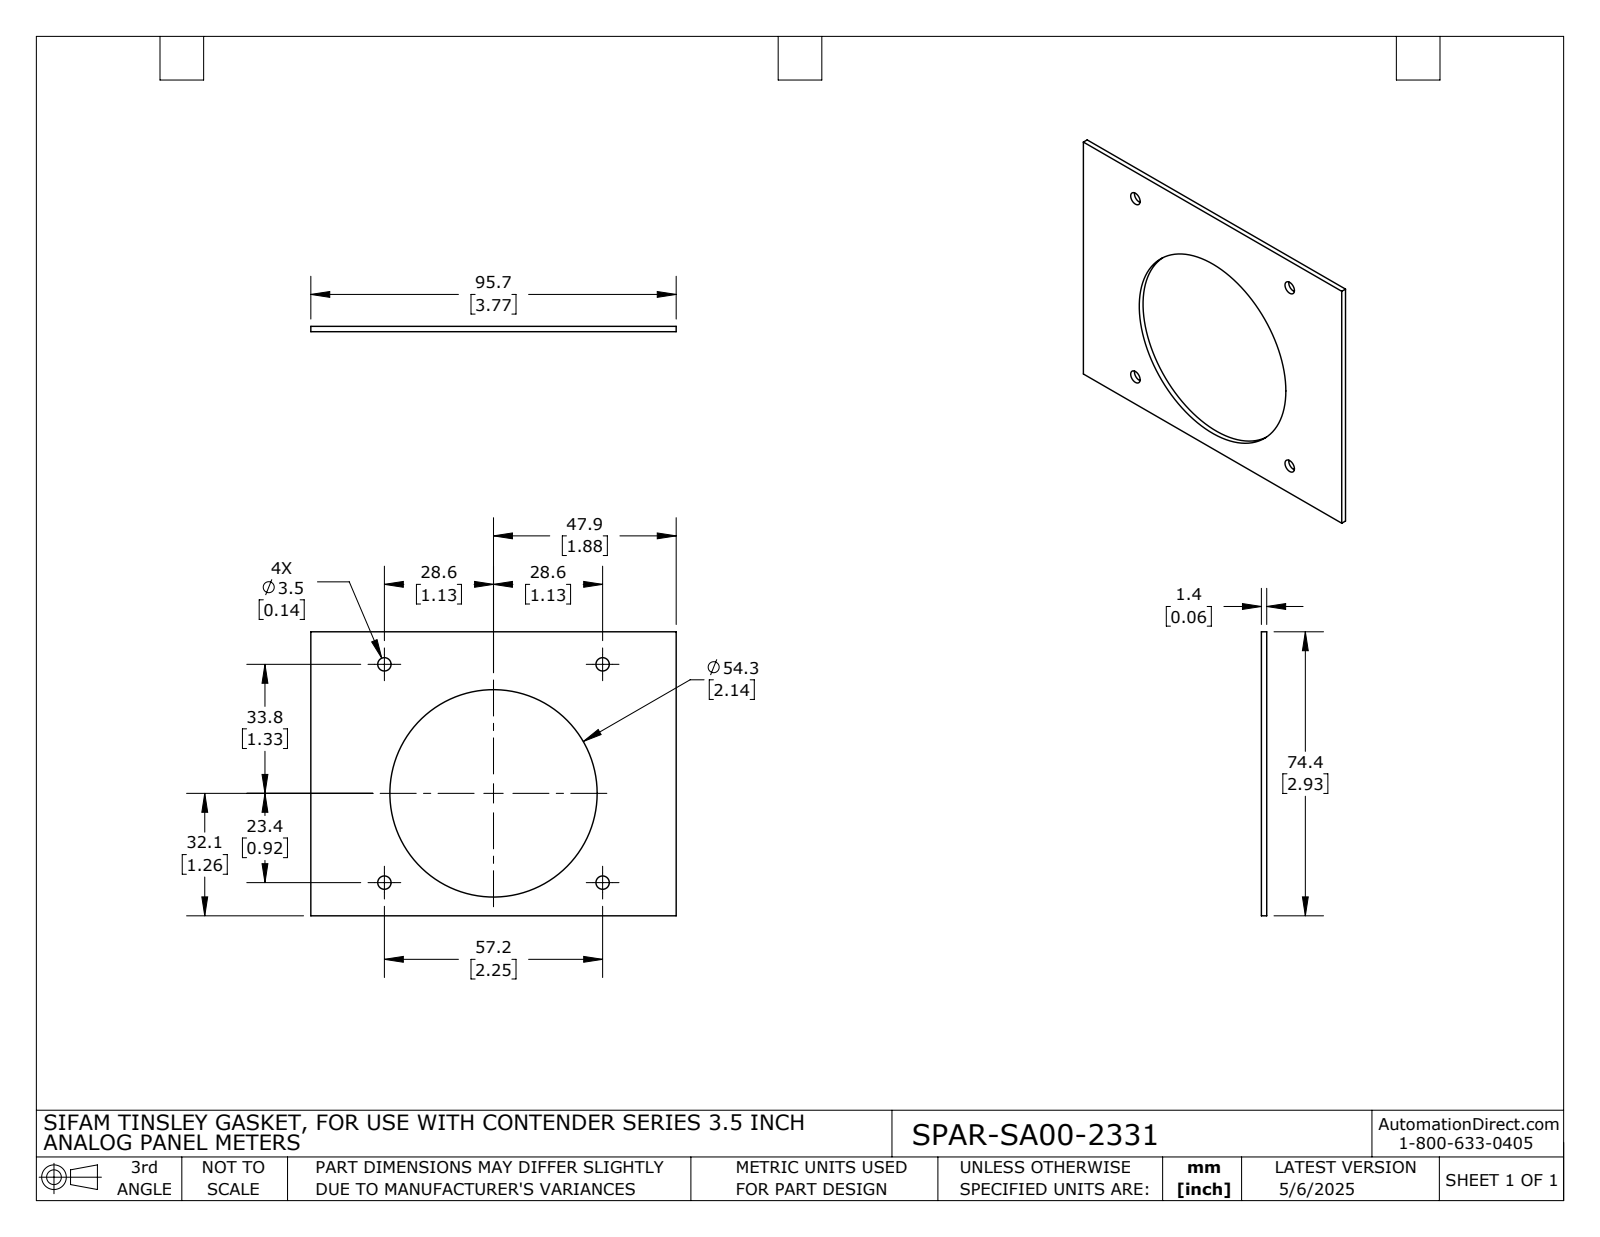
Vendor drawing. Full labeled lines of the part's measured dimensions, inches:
Part name (STEP PRODUCT): SPAR-SA00-2331
STEP written by: SolidWorks 2021 (AUTOMOTIVE_DESIGN)
Units: inches
Bodies: 1 solid, 16 faces (6 planar, 10 cylindrical, 0 other)
Overall size (bounding box): 3.768 × 2.928 × 0.055
Volume: 0.407 in³ · Surface area: 15.97 in²
Round holes (diameter × count): ⌀0.138 ×4, ⌀2.138 ×1
Main face-to-face distances: 0.055, 2.928, 3.768
Hole centre spacings: 1.454, 1.742, 2.25, 2.25, 3.182
